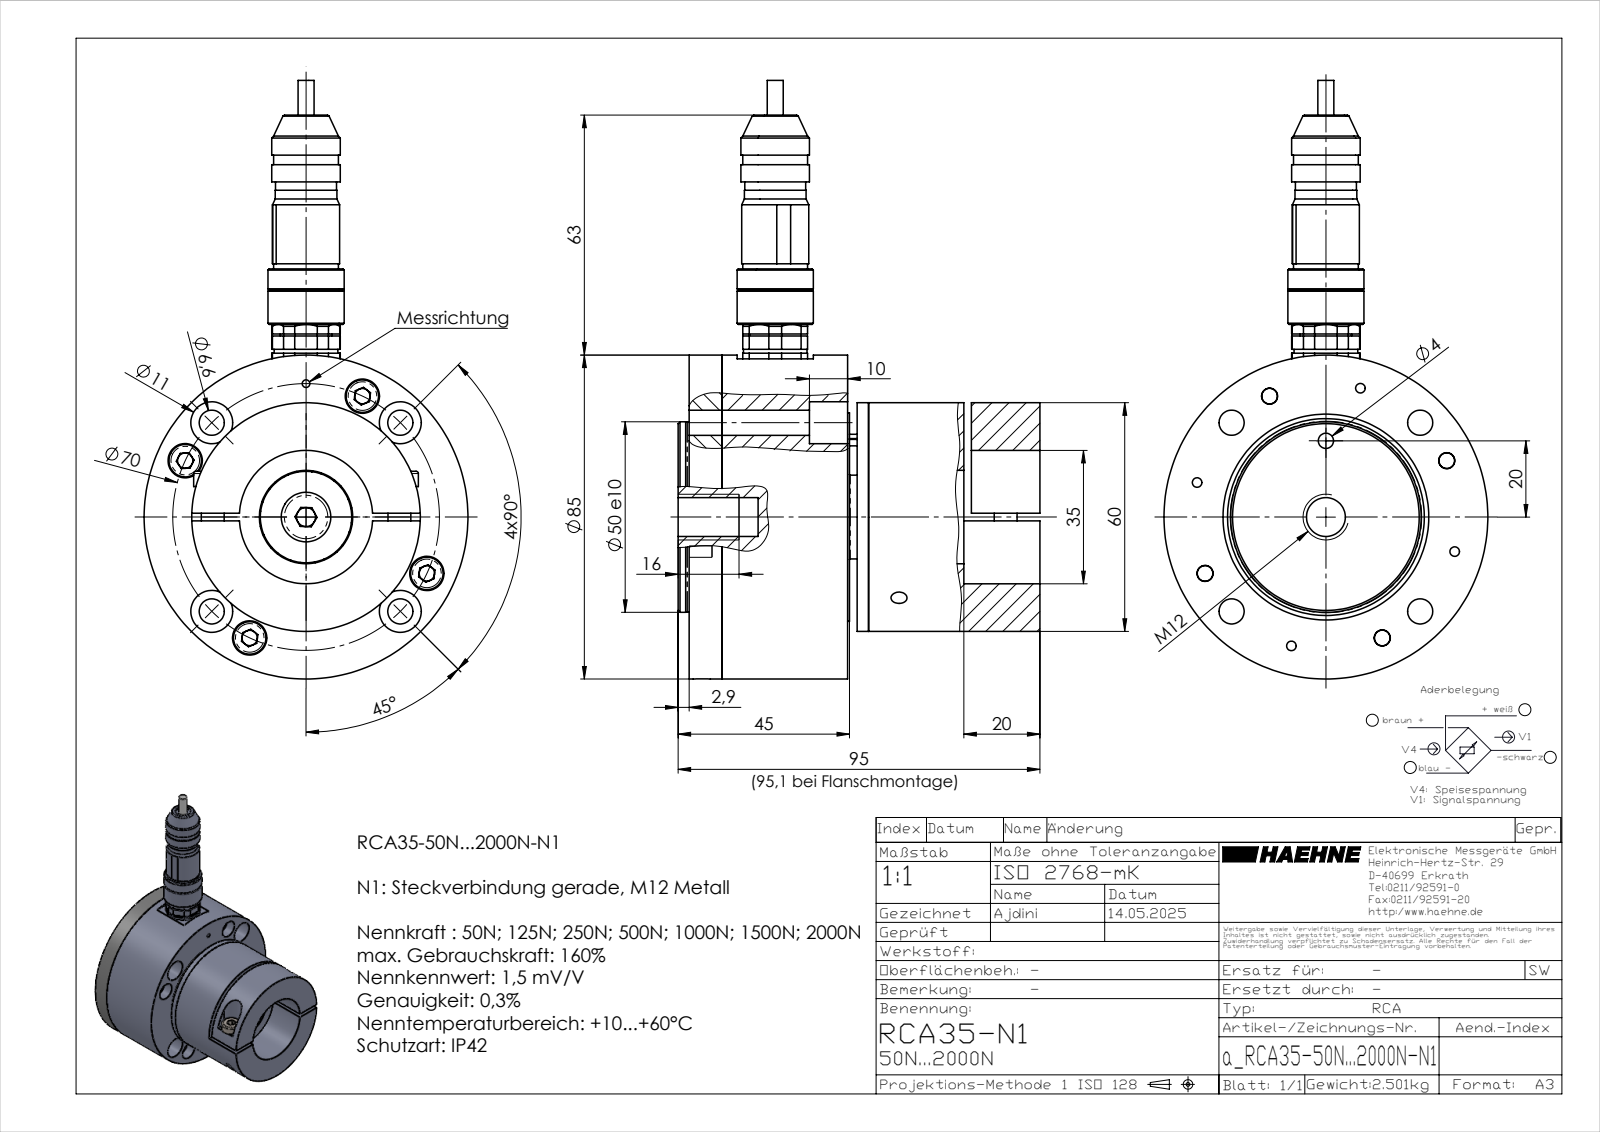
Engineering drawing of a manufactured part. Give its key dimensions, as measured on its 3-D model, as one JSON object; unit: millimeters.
{"part_name": "inafag_1203-tvh_7zkvytp7yxkimpdvw8sj0b5w4_07; inafag_1203-tvh_7zkvytp7yxkimpdvw8sj0b5w4_18; inafag_1203-tvh_7zkvytp7yxkimpdvw8sj0b5w4_08; DIN 7991 - M3 x 8 --- 4.8N_DIN 7991 - M3 x 8 --- 4.8N (+8 more)", "step_written_by": "SolidWorks 2023 (AUTOMOTIVE_DESIGN)", "units": "millimeters", "bodies": {"solids": 54, "faces": 743, "planar": 377, "cylindrical": 203, "other": 163}, "overall_size": [157.06, 95.1, 85], "volume_mm3": 364931, "surface_area_mm2": 113897, "round_holes": [[3.4, 9], [2.5, 8], [6.6, 6], [1, 5], [4.2, 5], [4, 4], [5.3, 4], [9, 4], [11, 4], [4.5, 2], [5, 2], [2, 1]], "round_bosses_or_shafts": [[3, 9], [5.7, 8], [8.5, 4], [5, 4], [1.5, 4], [1, 4], [17, 2], [10, 2]], "partial_cylinders_radius": [[0.3, 6], [1, 4], [5.5, 2], [0.57, 1], [0.6, 1], [0.77, 1], [3.5, 1]], "face_to_face_distances": [3, 8.6, 2, 47.1, 11.6, 30, 45, 50, 35.5, 38.5], "hole_center_spacings": [35, 49.5, 24.78, 25.2, 32.8, 51.14, 56.46, 2.5]}
